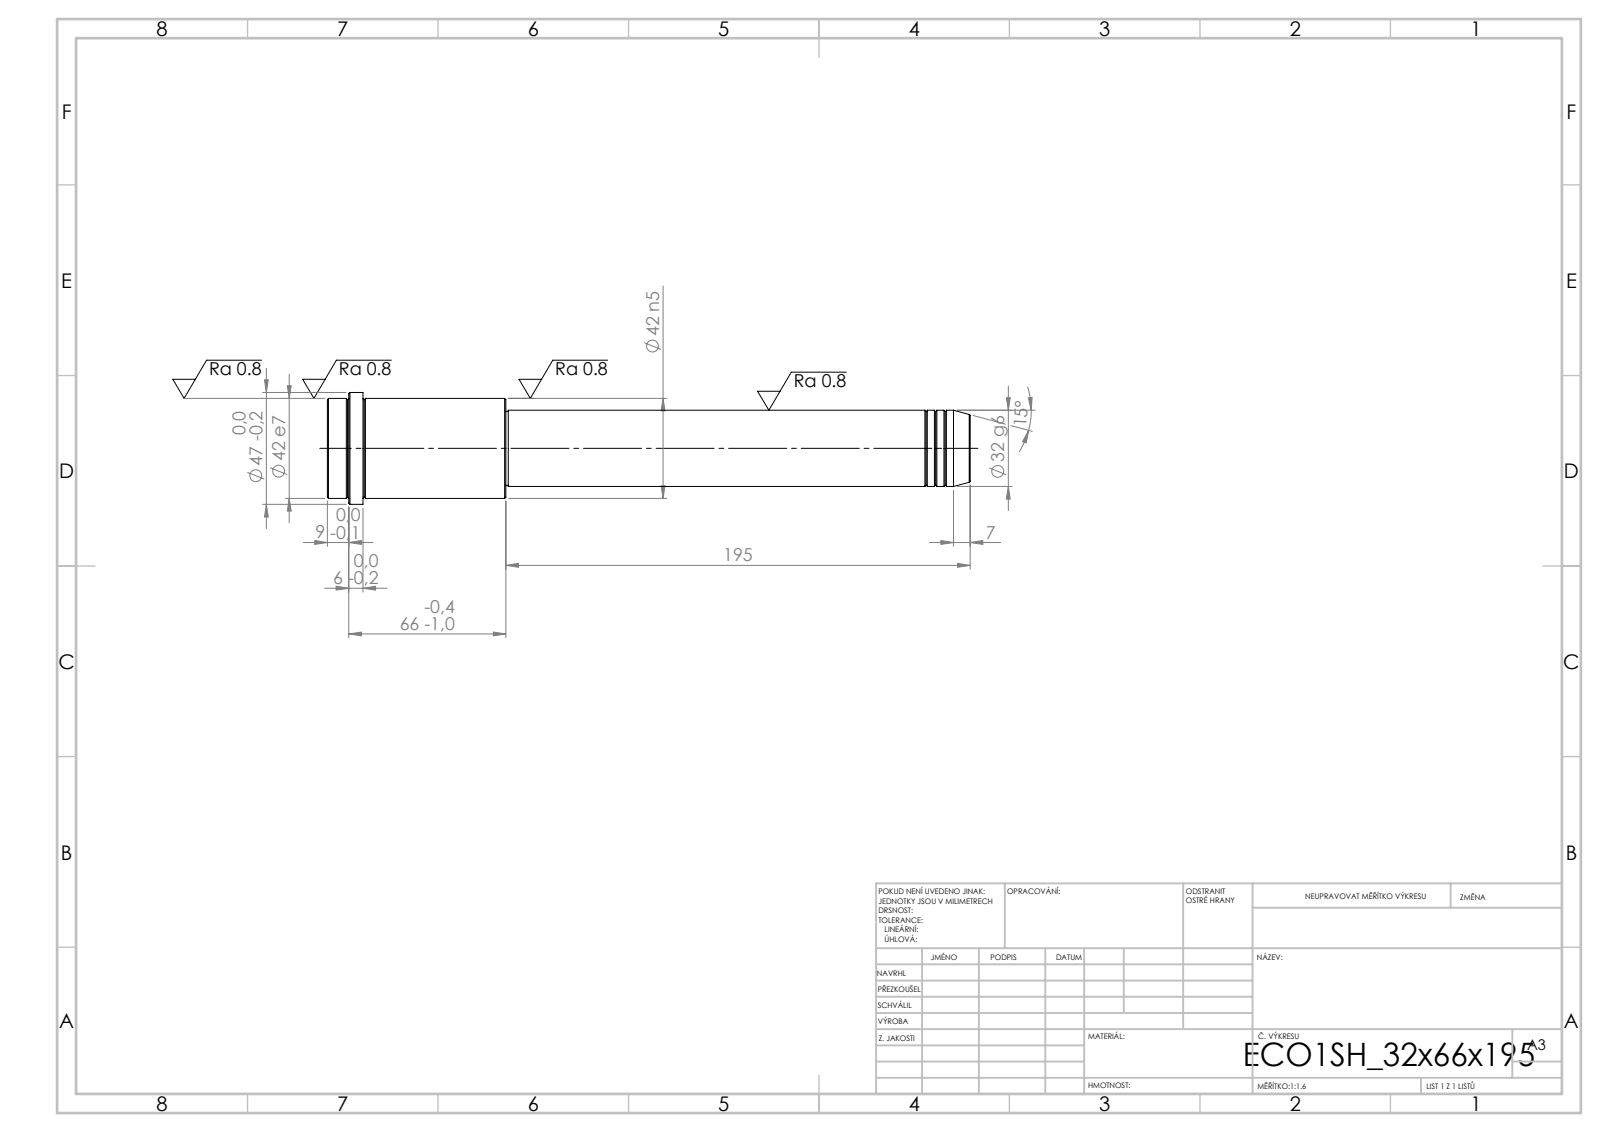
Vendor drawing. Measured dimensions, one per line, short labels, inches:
written by: SolidWorks 2019 (CONFIG_CONTROL_DESIGN)
unit: in
bodies: 1 solid, 52 faces (6 planar, 16 cylindrical, 30 other)
size: 10.63 × 1.85 × 1.85
volume: 15.98 in³; area: 51.37 in²
bosses: 1× ⌀1.85, 1× ⌀1.654, 1× ⌀1.26, 1× ⌀1.22
face distances: 10.63, 7.677, 2.953, 10.039, 2.362, 0.591, 10.276, 2.598, 0.236, 0.354
